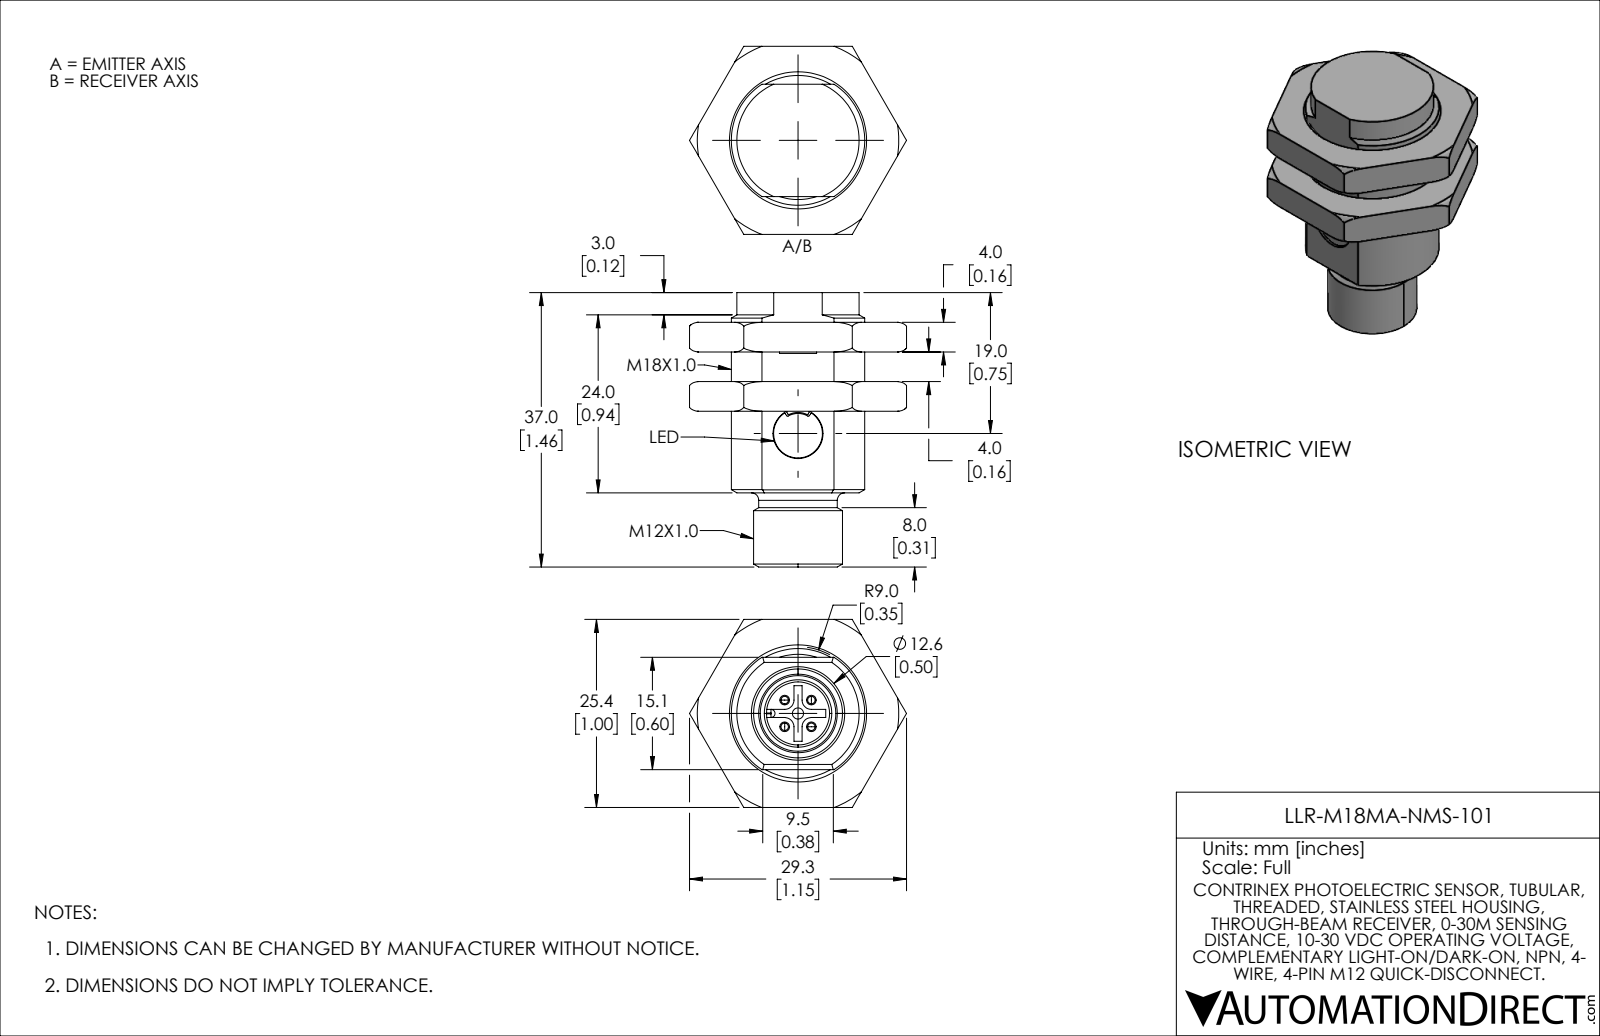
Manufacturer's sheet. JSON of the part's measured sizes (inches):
{"part_name": "LLR-M18MA-NMS-101", "step_written_by": "SolidWorks 2021 (AUTOMOTIVE_DESIGN)", "units": "inches", "bodies": {"solids": 3, "faces": 176, "planar": 65, "cylindrical": 50, "other": 61}, "overall_size": [1.457, 1.153, 0.998], "volume_in3": 0.572, "surface_area_in2": 7.737, "round_holes": [[0.059, 1], [0.266, 1], [0.335, 1], [0.689, 1]], "round_bosses_or_shafts": [[0.039, 4], [0.472, 1], [0.417, 1]], "partial_cylinders_radius": [[0.004, 4], [0.006, 4], [0.049, 4], [0.02, 2], [0.022, 1], [0.106, 1], [0.112, 1], [0.325, 1]], "face_to_face_distances": [0.157, 0.315, 0.472, 0.998, 0.201, 0.798, 0.597, 0.63, 0.433, 0.591]}
